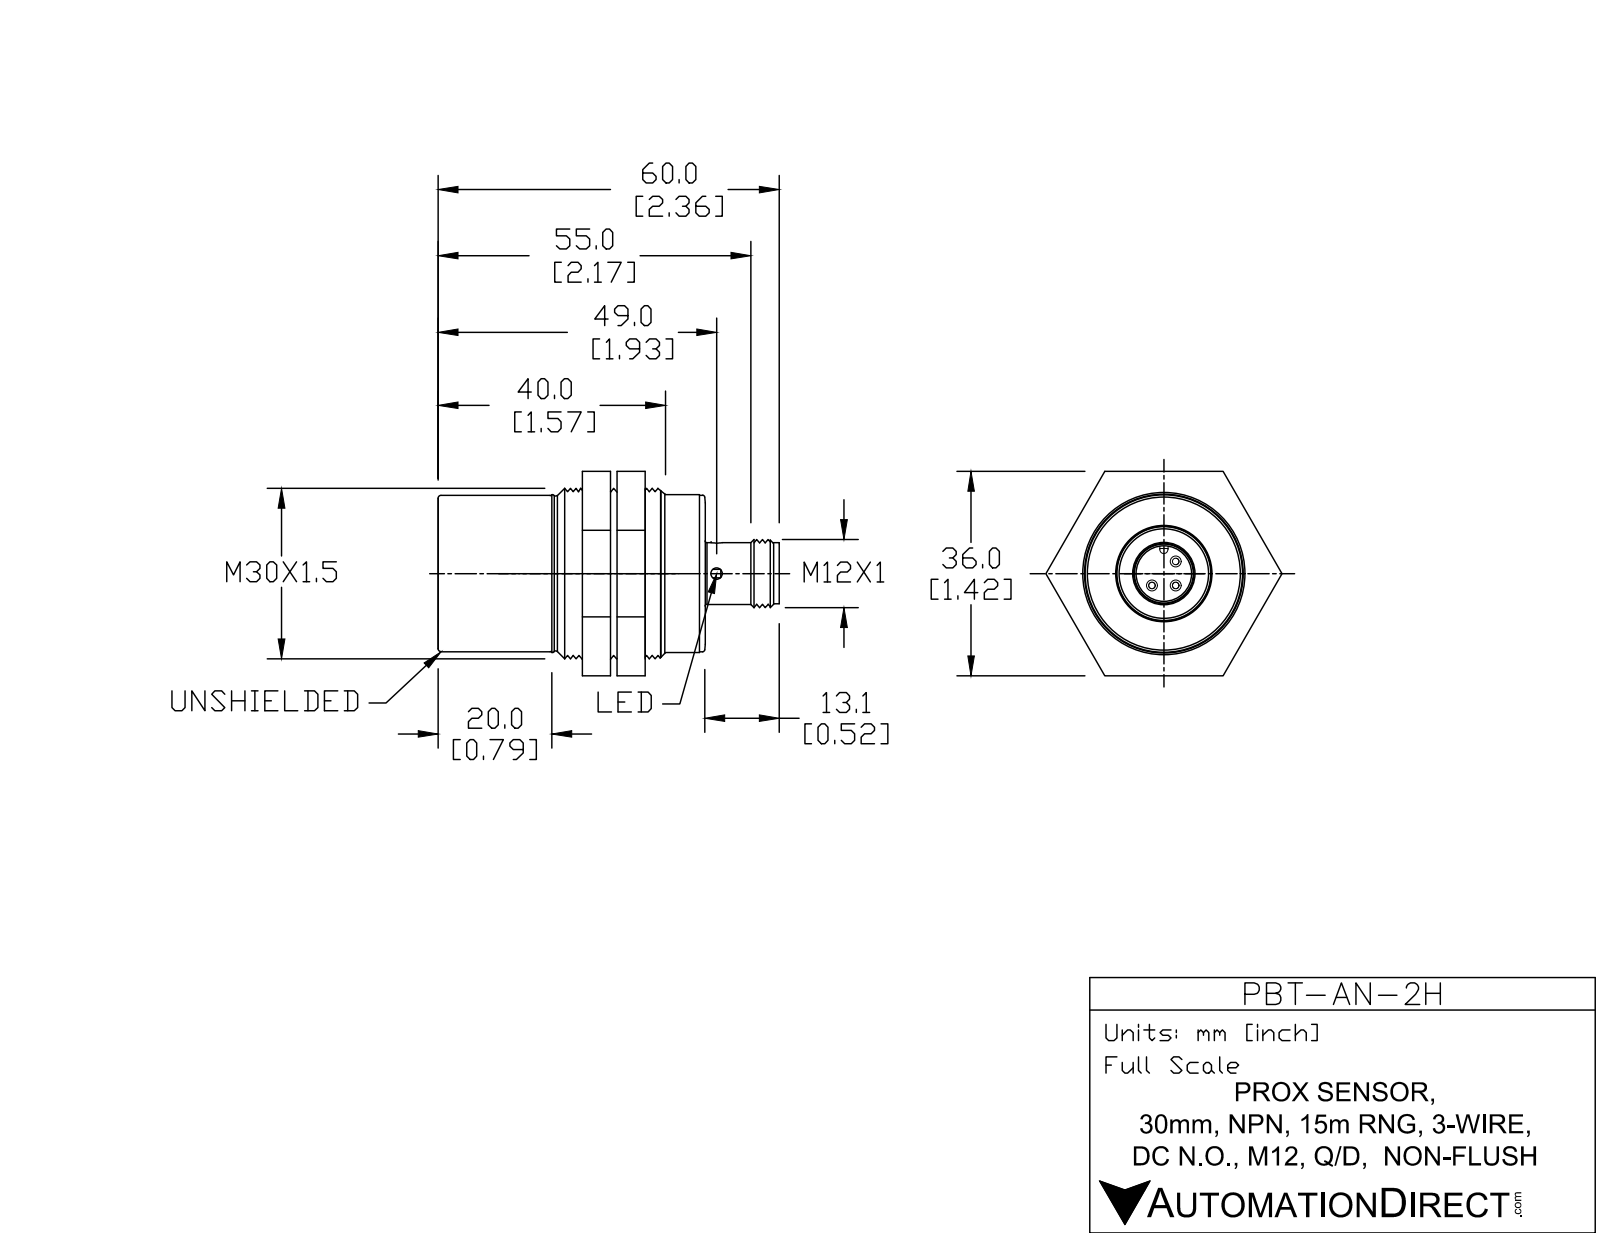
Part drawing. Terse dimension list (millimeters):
name: PBT-AN-2H
written by: SolidWorks 2011 (AUTOMOTIVE_DESIGN)
unit: mm
bodies: 8 solids, 67 faces (39 planar, 18 cylindrical, 10 other)
size: 59.5 × 41.55 × 36.66
volume: 35 044 mm³; area: 11 837 mm²
holes: 1× ⌀1.25, 1× ⌀8.5, 1× ⌀10.75, 1× ⌀28.5
bosses: 3× ⌀1, 1× ⌀30, 1× ⌀28, 1× ⌀27.5, 1× ⌀27.46, 1× ⌀12, 1× ⌀10.9, 1× ⌀10.55
rounds: 1× R0.5
face distances: 10, 20, 27, 4.5, 14.5, 47, 12.5, 37, 22.5, 32.5
